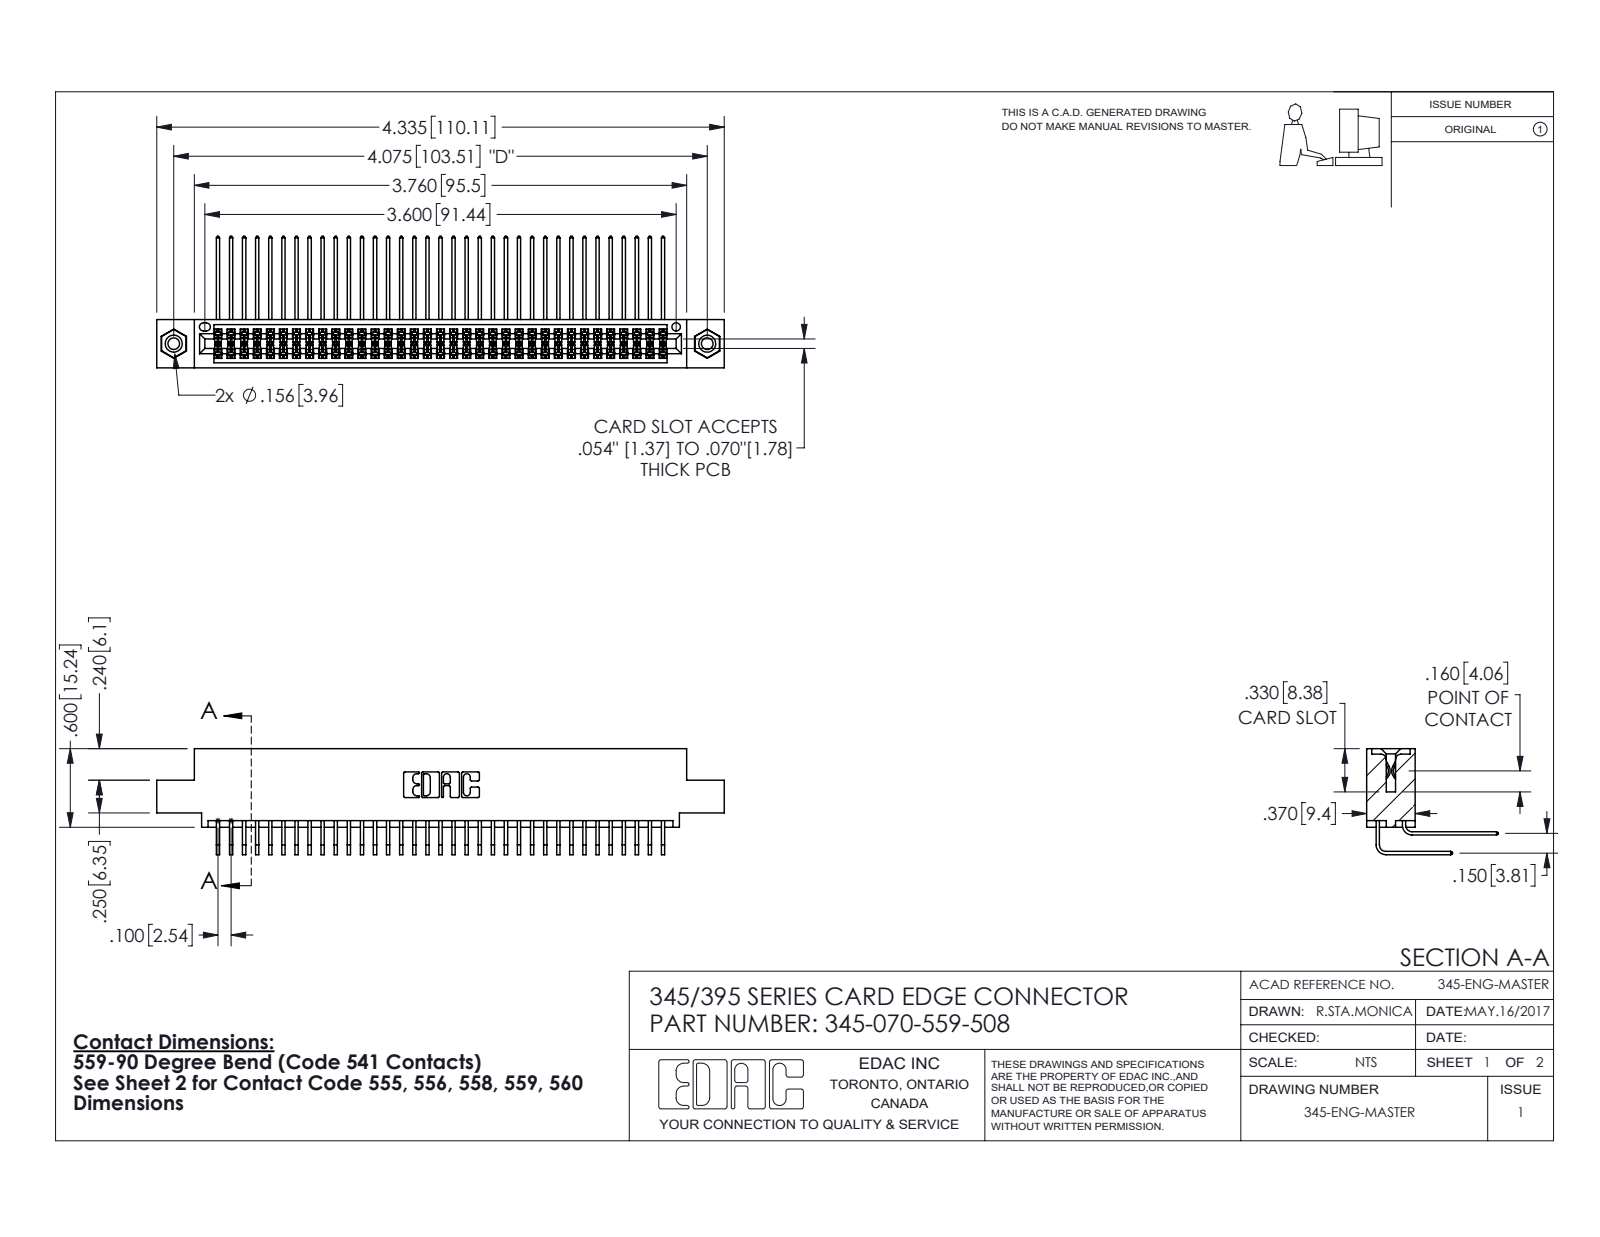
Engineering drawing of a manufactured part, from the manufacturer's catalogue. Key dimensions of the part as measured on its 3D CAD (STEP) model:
Part name (STEP PRODUCT): 345-292-001_559 Tail - 2; 345-250-001_345-250-003-102; 345-070-559-508; 345 Part_0.110 Offset - 0.156 Dia-TI (+1 more)
STEP written by: SolidWorks 2016 (CONFIG_CONTROL_DESIGN)
Units: inches
Bodies: 73 solids, 3830 faces (2566 planar, 1248 cylindrical, 16 other)
Overall size (bounding box): 4.335 × 1.005 × 0.809
Volume: 0.669 in³ · Surface area: 28 in²
Round holes (diameter × count): ⌀0.089 ×2, ⌀0.125 ×2, ⌀0.156 ×2, ⌀0.064 ×1
Round bosses / shafts (diameter × count): ⌀0.155 ×2
Partial cylindrical surfaces — rounded edges, fillets, slot ends (radius × count): R0.006 ×139, R0.01 ×22, R0.007 ×6, R0.031 ×6, R0.026 ×3, R0.014 ×2, R0.019 ×2, R0.022 ×2
Main face-to-face distances: 0.072, 0.298, 0.37, 0.2, 0.098, 0.272, 0.025, 0.225, 0.175, 0.15
Hole centre spacings: 0.27, 3.839, 4.075
